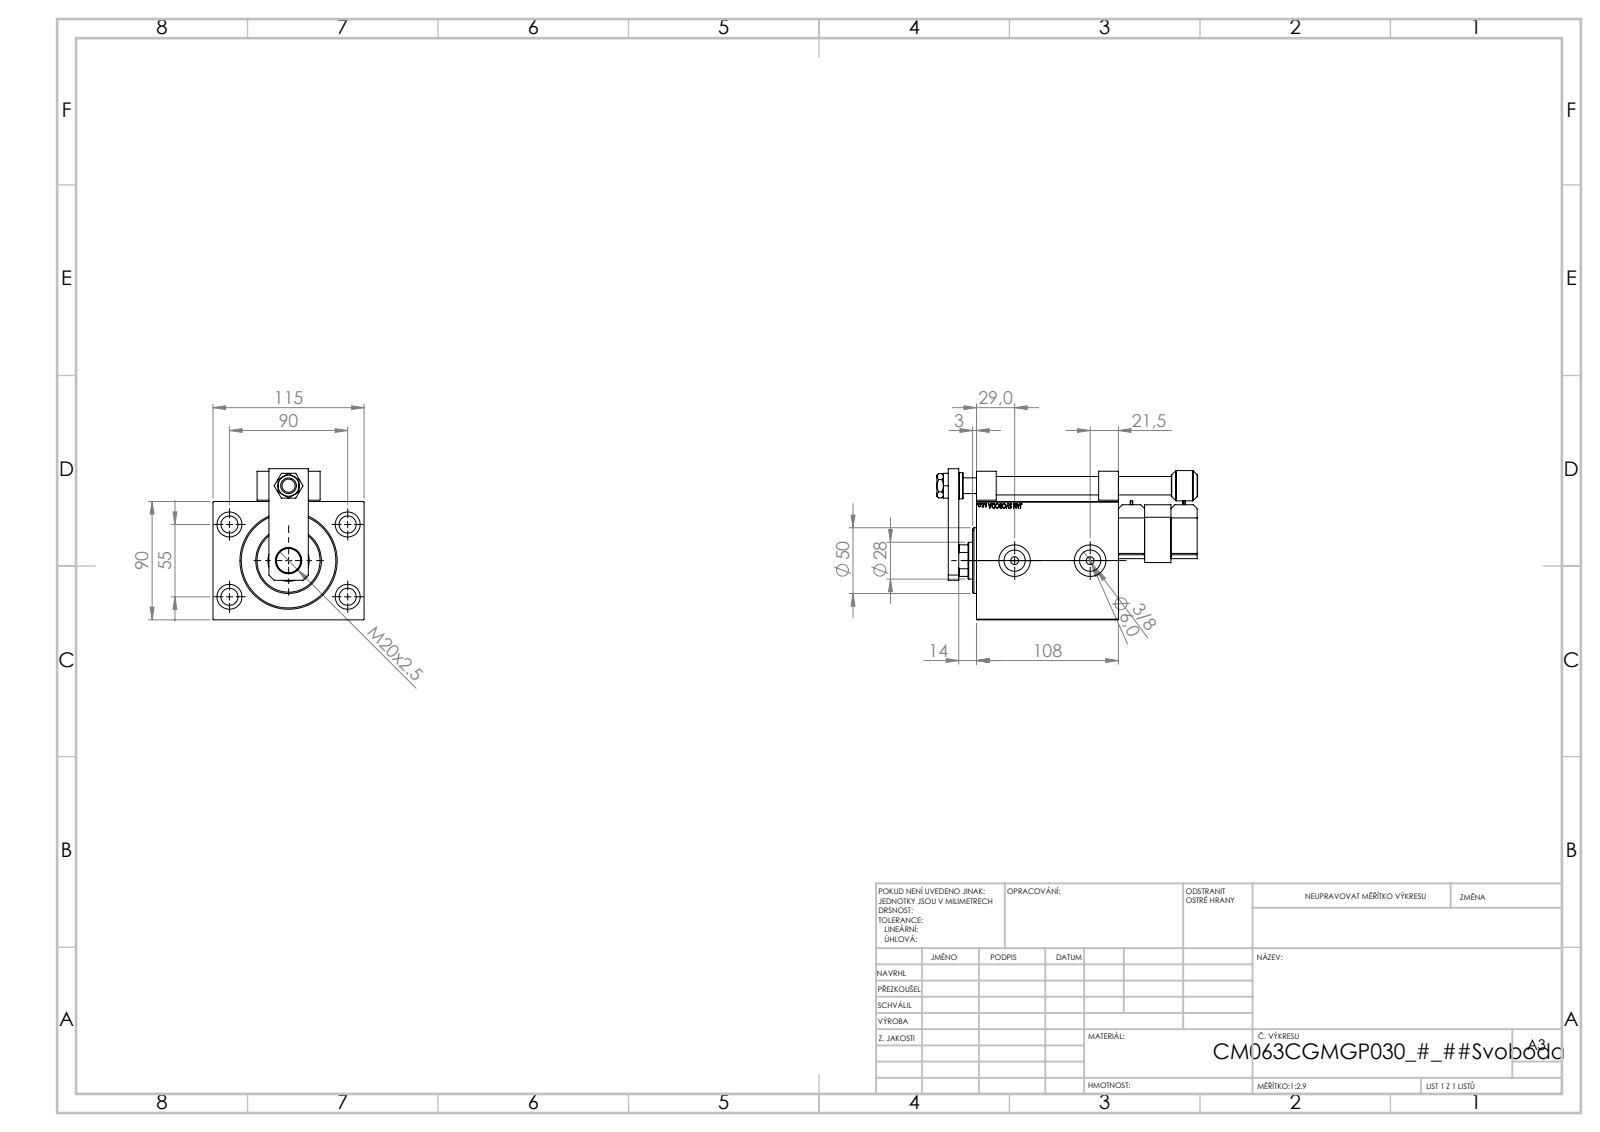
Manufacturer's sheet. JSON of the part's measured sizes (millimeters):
{"part_name": "SWITCH DIM W_B; NUT_D16; ZARAZKA_P; SWITCH P (+7 more)", "step_written_by": "SolidWorks 2019 (CONFIG_CONTROL_DESIGN)", "units": "millimeters", "bodies": {"solids": 14, "faces": 1090, "planar": 521, "cylindrical": 120, "other": 449}, "overall_size": [198.5, 115, 115], "volume_mm3": 1143000, "surface_area_mm2": 187436, "round_holes": [[13, 5], [4, 4], [8, 4], [19, 4], [6, 2], [16.17, 2], [24, 2], [12, 1], [14, 1], [18.5, 1], [20, 1], [28, 1]], "round_bosses_or_shafts": [[20, 3], [16, 2], [14, 2], [6, 2], [50, 1], [23, 1]], "partial_cylinders_radius": [[3, 1], [13.5, 1]], "face_to_face_distances": [90, 115, 20, 108, 17.5, 37.5, 90.5, 40, 13.5, 77.5], "hole_center_spacings": [52.74, 20, 53.81, 55, 90, 93, 95.13, 95.74]}
